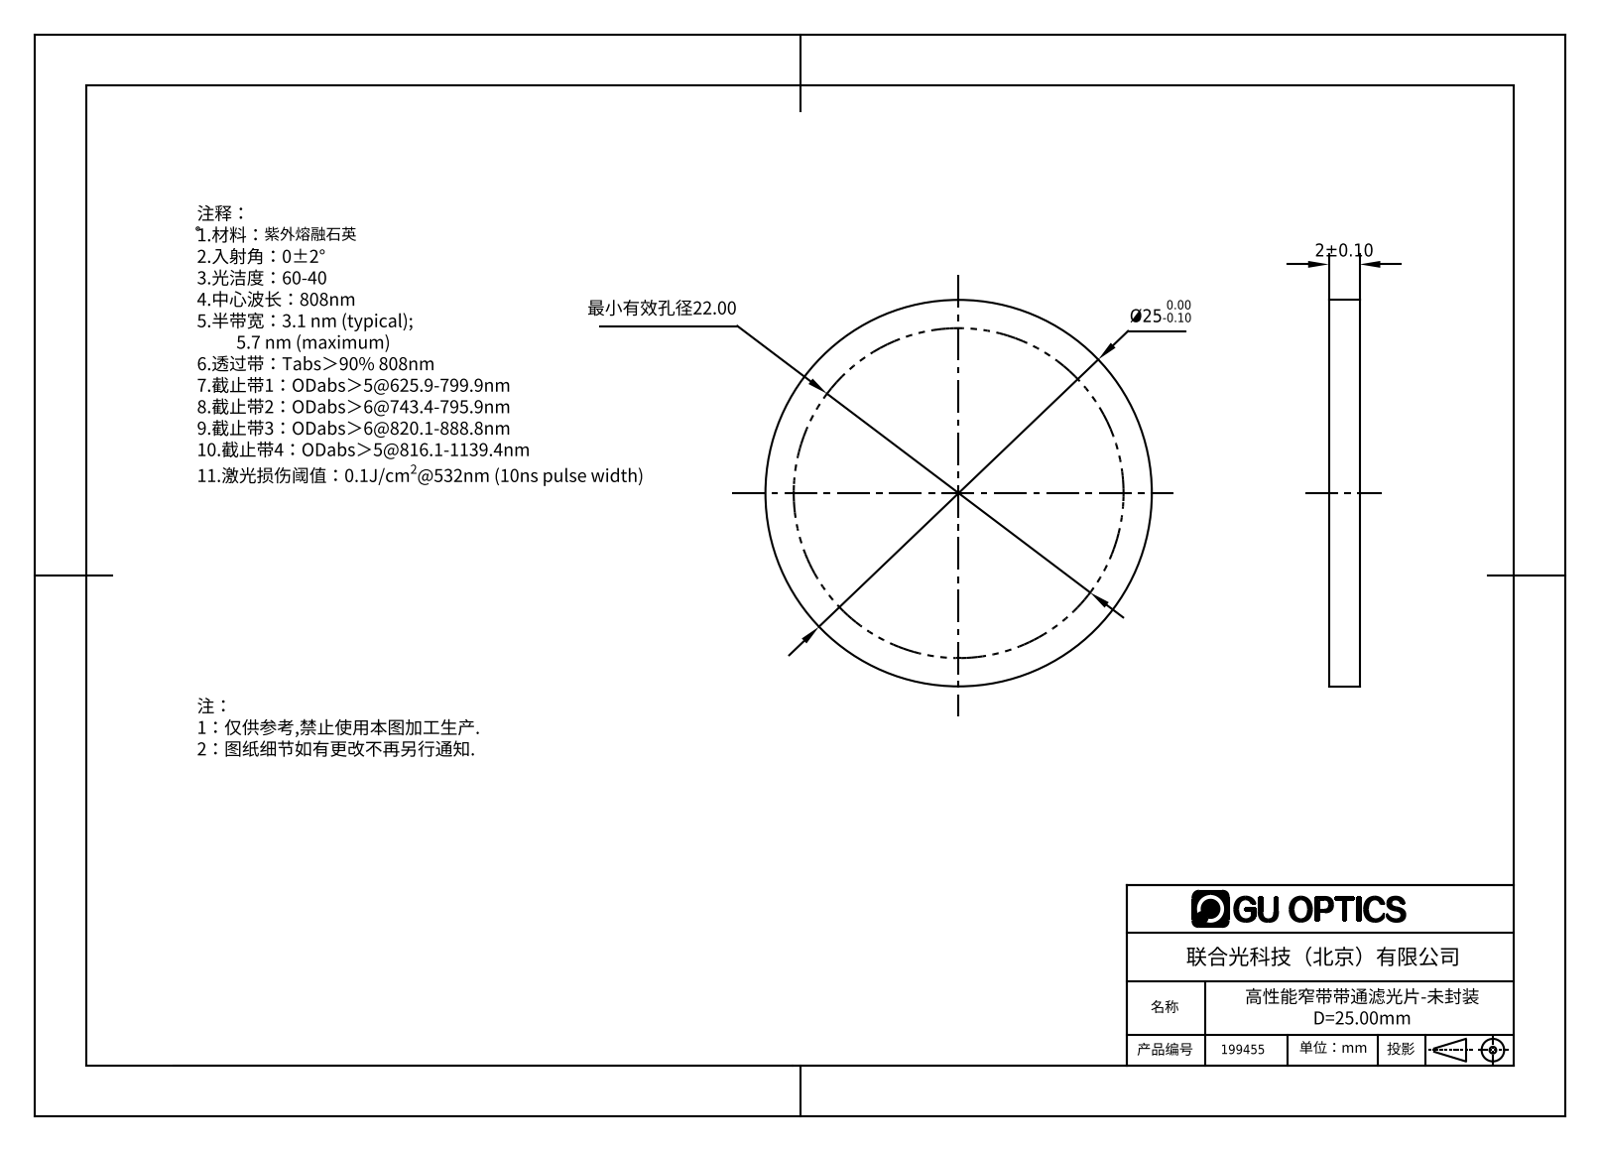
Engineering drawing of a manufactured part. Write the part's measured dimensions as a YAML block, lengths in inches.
part_name: "199448"
step_written_by: "SolidWorks 2019 (CONFIG_CONTROL_DESIGN)"
units: inches
bodies: {solids: 1, faces: 4, planar: 2, cylindrical: 2, other: 0}
overall_size: [0.984, 0.984, 0.079]
volume: 0.06
surface_area: 1.765
round_bosses_or_shafts:
  - {diameter: 0.984, count: 1}
face_to_face_distances: [0.079]
